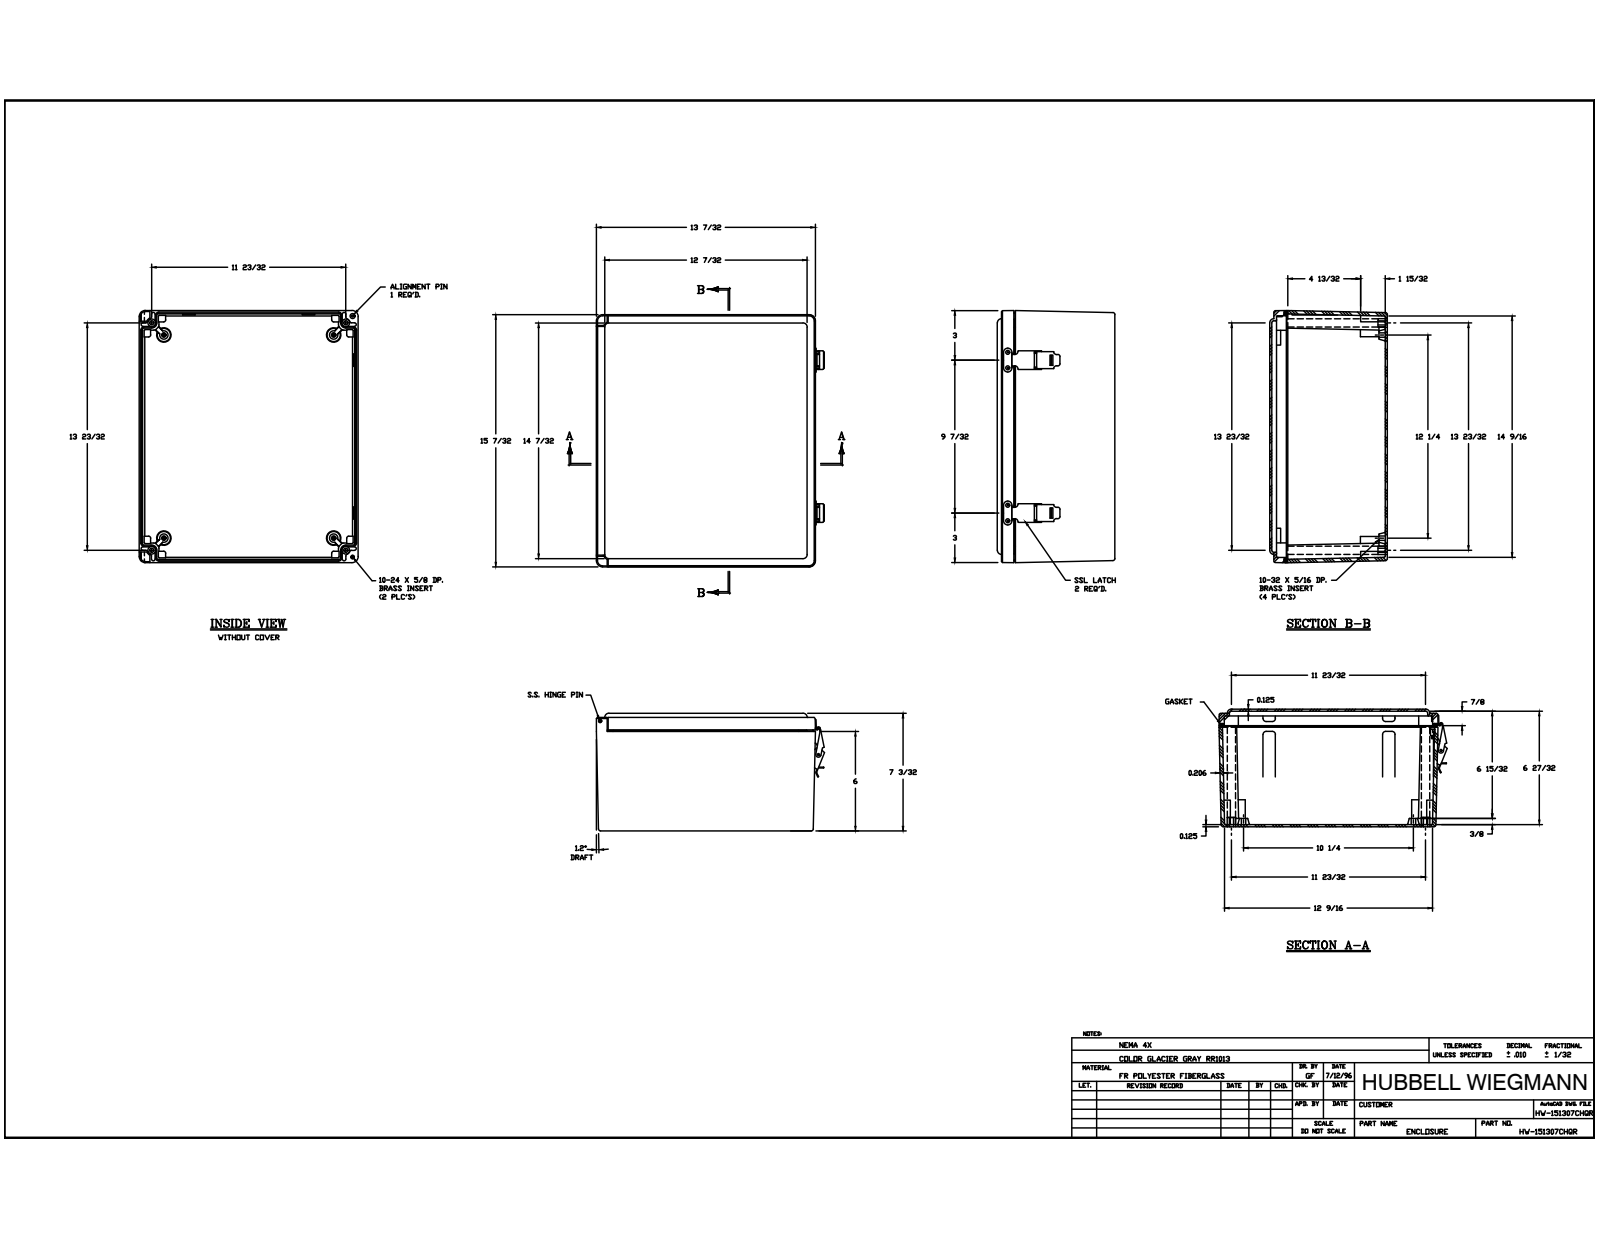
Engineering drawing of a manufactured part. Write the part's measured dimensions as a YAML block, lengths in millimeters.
part_name: "WP1513HPLBOX; 0.3125-18 X 0.563 DP BRASS INSERT; 10-32 X0.3125 DP BRASS INSERT; 10-24 X 0.625 DP BRASS INSERT (+8 more)"
step_written_by: "Autodesk Inventor 2014 (AUTOMOTIVE_DESIGN)"
units: millimeters
bodies: {solids: 41, faces: 1324, planar: 541, cylindrical: 475, other: 308}
overall_size: [386.59, 351.6, 180.18]
volume: 2288000
surface_area: 1104000
round_holes:
  - {diameter: 2.64, count: 8}
  - {diameter: 3.56, count: 8}
  - {diameter: 7.14, count: 6}
  - {diameter: 3.3, count: 4}
  - {diameter: 3.96, count: 4}
  - {diameter: 3.97, count: 4}
  - {diameter: 7.94, count: 4}
  - {diameter: 13.49, count: 4}
  - {diameter: 2.44, count: 2}
  - {diameter: 3.43, count: 2}
  - {diameter: 3.68, count: 2}
  - {diameter: 4.55, count: 2}
round_bosses_or_shafts:
  - {diameter: 9.52, count: 2}
  - {diameter: 9.42, count: 2}
  - {diameter: 5.94, count: 2}
  - {diameter: 2.42, count: 2}
  - {diameter: 7.62, count: 1}
  - {diameter: 7.6, count: 1}
  - {diameter: 4.7, count: 1}
  - {diameter: 4.52, count: 1}
partial_cylinders:
  - {radius: 0.79, count: 60}
  - {radius: 3.17, count: 40}
  - {radius: 1.59, count: 29}
  - {radius: 1.14, count: 16}
  - {radius: 0.76, count: 12}
  - {radius: 6.35, count: 12}
  - {radius: 0.57, count: 9}
  - {radius: 0.38, count: 8}
face_to_face_distances: [3.17, 177.01, 4.72, 180.18, 173.84, 3.18, 6.35, 173.83, 170.66, 19.05]
hole_center_spacings: [233.36, 14.58, 26.39, 40.97, 279.66, 290.8, 308.18, 330.37]
